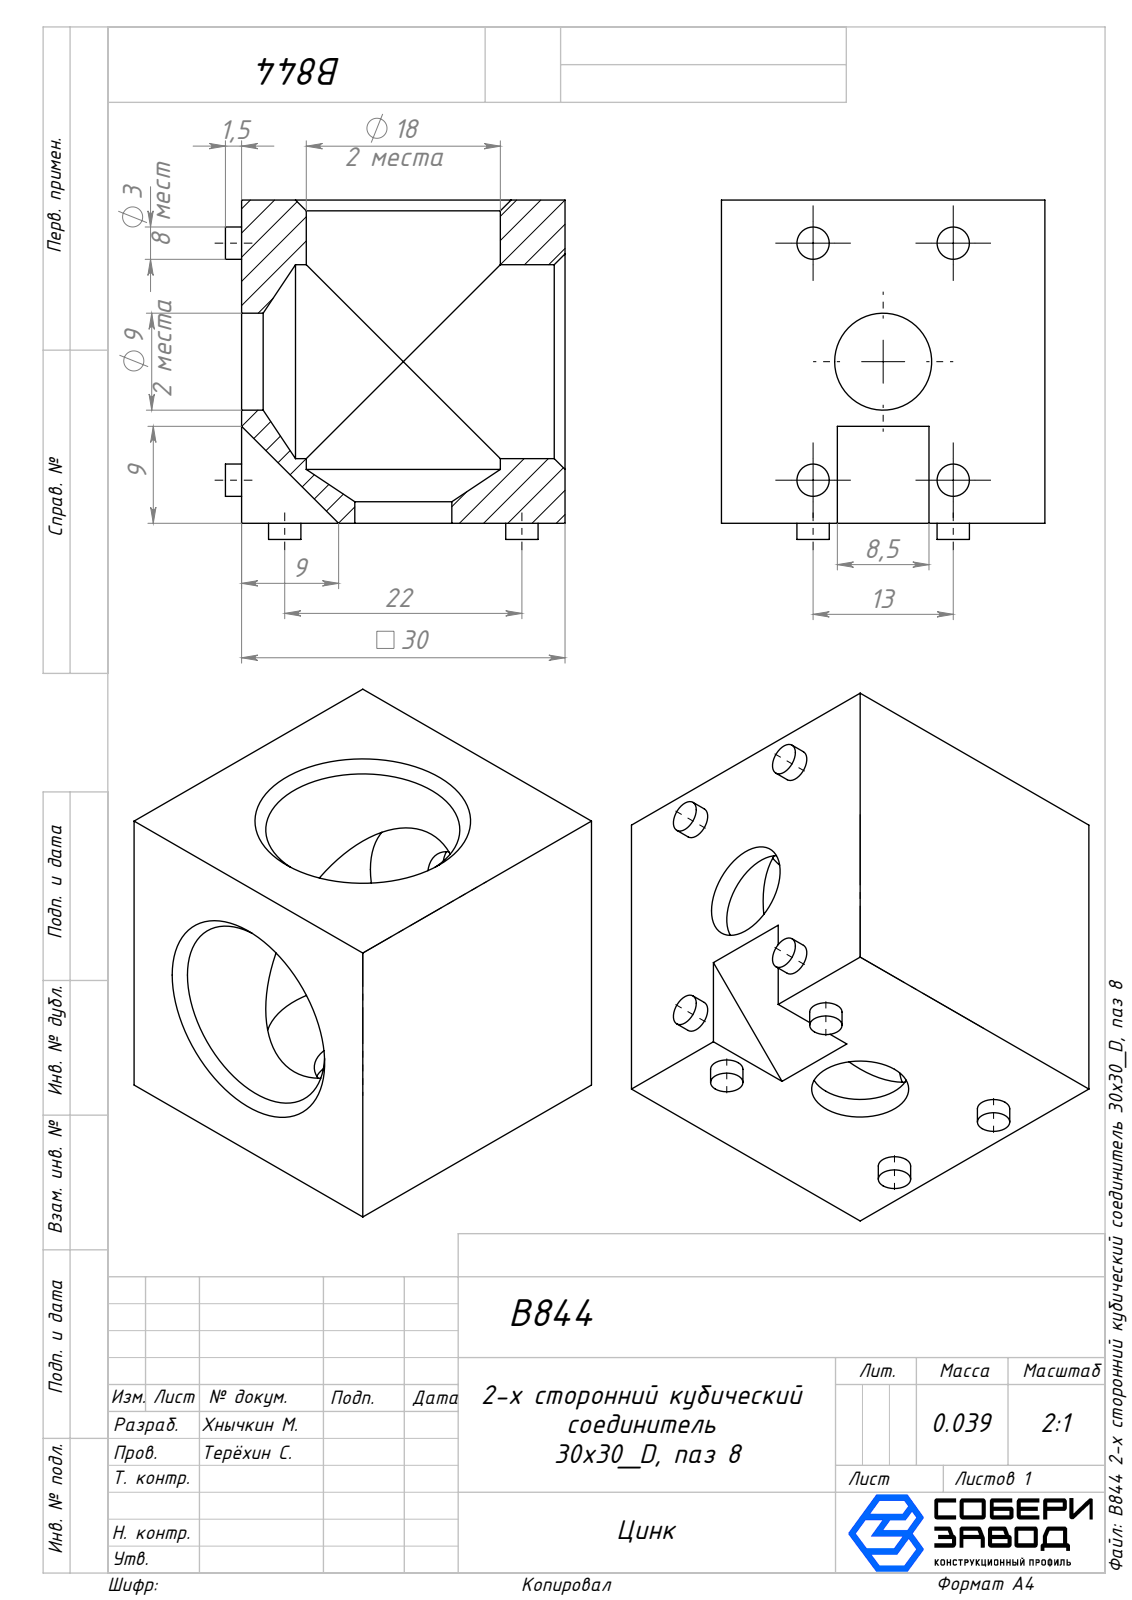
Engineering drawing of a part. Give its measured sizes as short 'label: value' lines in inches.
name: B844 2-х сторонний кубический соединитель 30х30_D, паз 8
written by: SolidWorks 2025 (AUTOMOTIVE_DESIGN)
unit: in
bodies: 1 solid, 48 faces (14 planar, 26 cylindrical, 8 other)
size: 1.24 × 1.24 × 1.181
volume: 1.03 in³; area: 10.72 in²
holes: 2× ⌀0.709, 1× ⌀0.354
bosses: 8× ⌀0.118
face distances: 1.181, 0.059, 1.24
